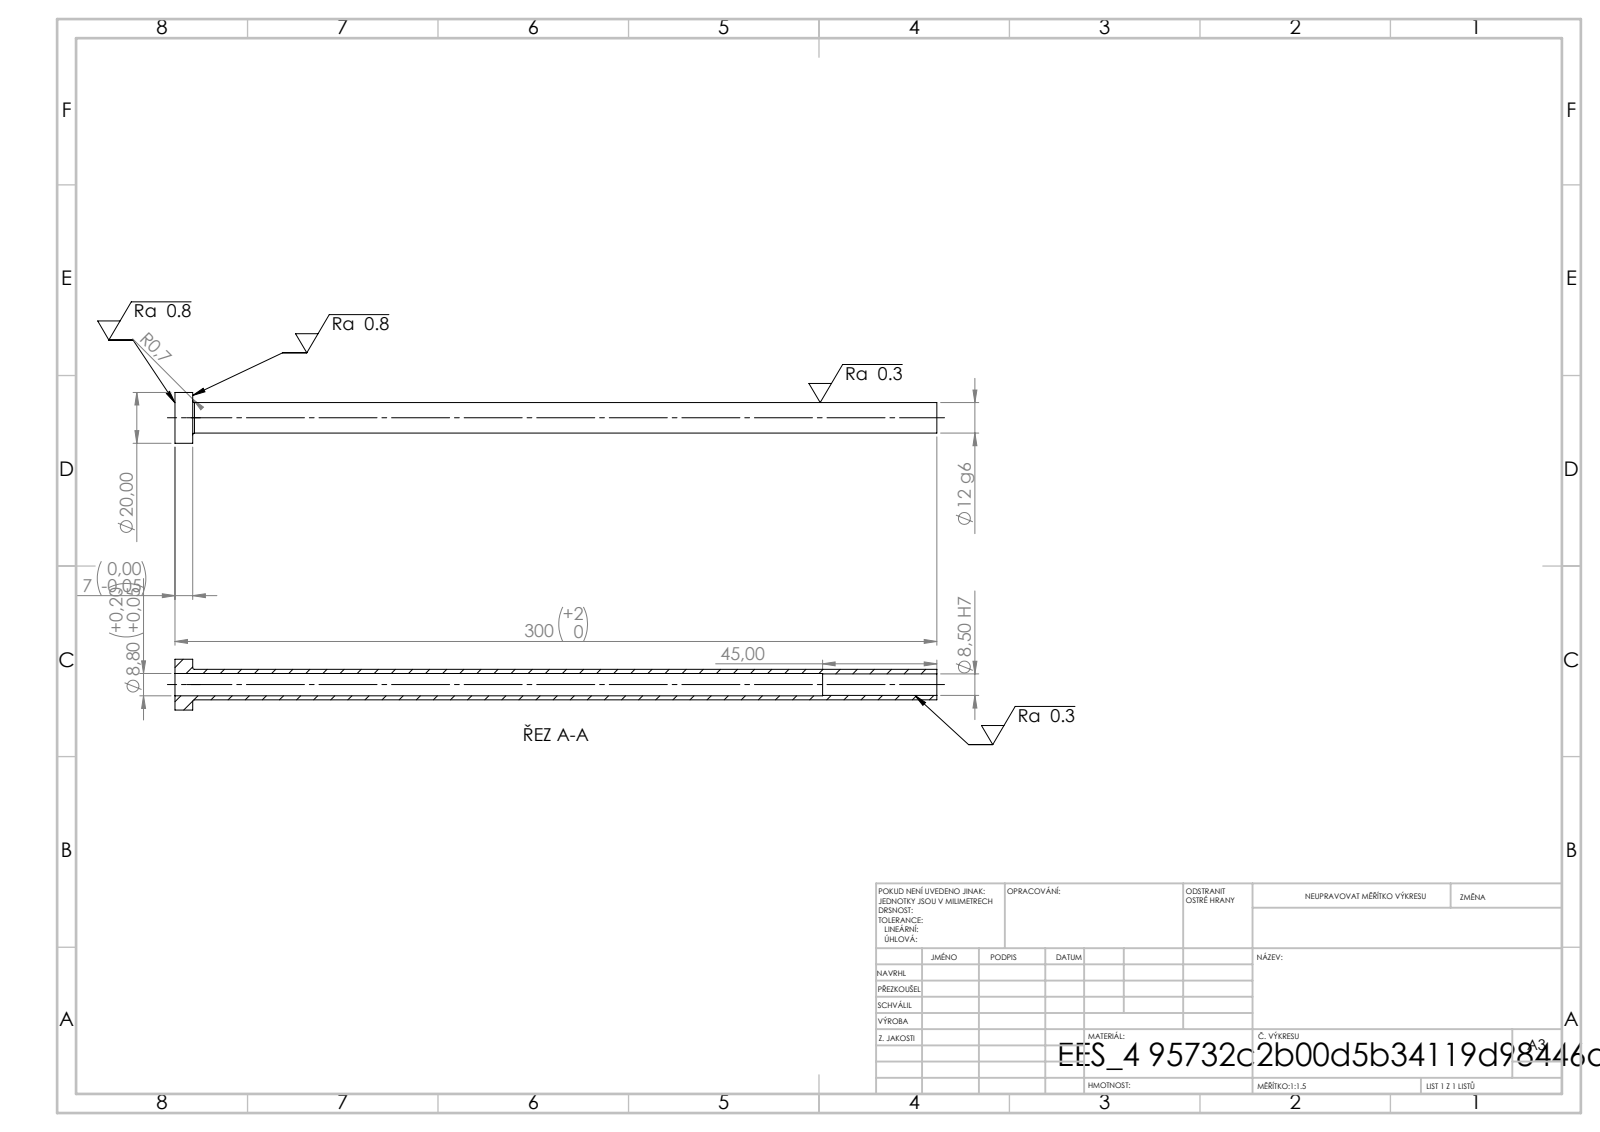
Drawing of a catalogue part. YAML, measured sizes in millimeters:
step_written_by: "SolidWorks 2019 (CONFIG_CONTROL_DESIGN)"
units: millimeters
bodies: {solids: 1, faces: 14, planar: 4, cylindrical: 8, other: 2}
overall_size: [300, 20, 20]
volume: 17278
surface_area: 20241
round_holes:
  - {diameter: 8.5, count: 1}
  - {diameter: 8.8, count: 1}
round_bosses_or_shafts:
  - {diameter: 20, count: 1}
  - {diameter: 12, count: 1}
face_to_face_distances: [7, 300, 293, 255, 248, 45]
